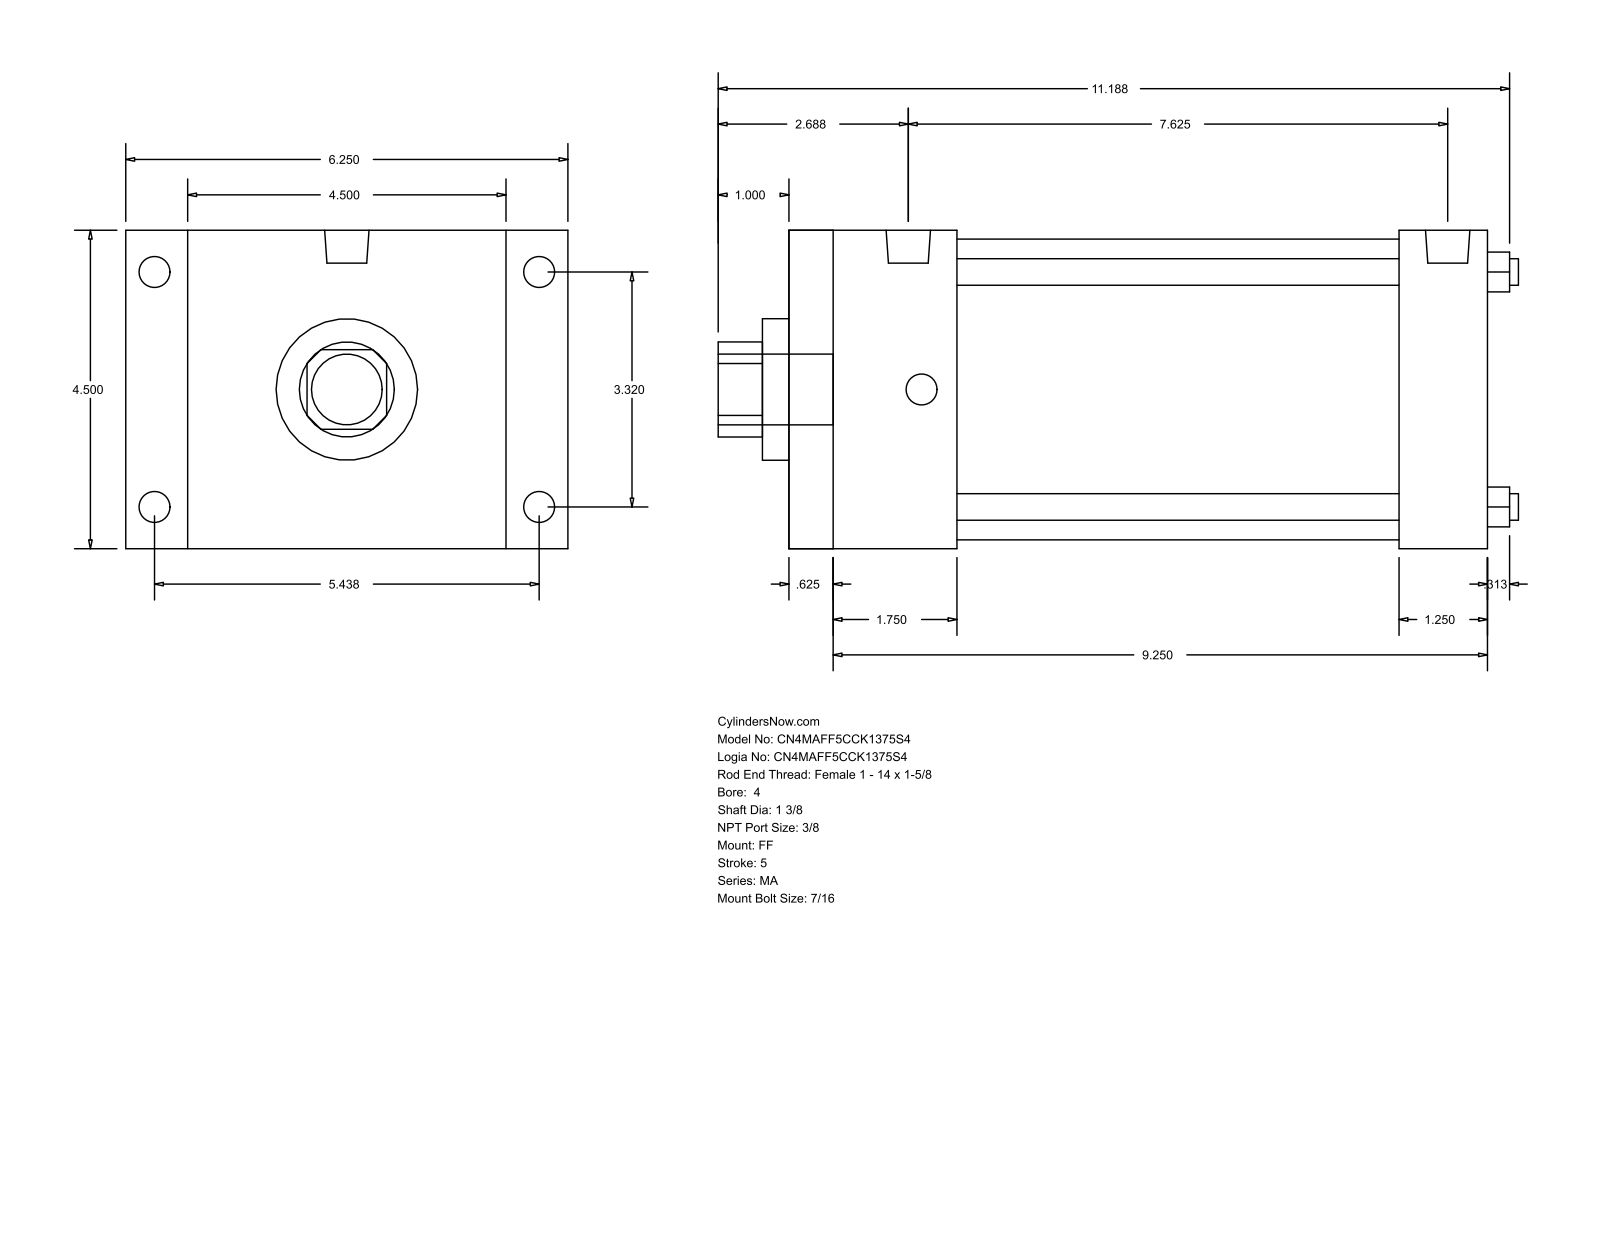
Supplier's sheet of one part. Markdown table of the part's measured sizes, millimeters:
| quantity | value |
| --- | --- |
| part name | MA_FF__0400_1.375 |
| STEP written by | GSSL Pune (CONFIG_CONTROL_DESIGN) |
| units | millimeters |
| bodies | 0 solids, 92 faces (64 planar, 28 cylindrical, 0 other) |
| overall size | 287.34 × 158.75 × 114.3 |
| round holes (diameter × count) | 9.53 × 4, 34.92 × 1, 50.8 × 1, 107.95 × 1 |
| round bosses / shafts (diameter × count) | 11.11 × 8, 15.93 × 2, 25.4 × 1 |
| partial cylindrical surfaces (radius × count) | 17.06 × 1 |
| main face-to-face distances | 114.3, 250.83, 15.87, 234.96, 22.23, 136.53, 219.07, 203.2, 31.76, 60.32 |
| hole center spacings | 59.62, 84.32, 119.25 |
